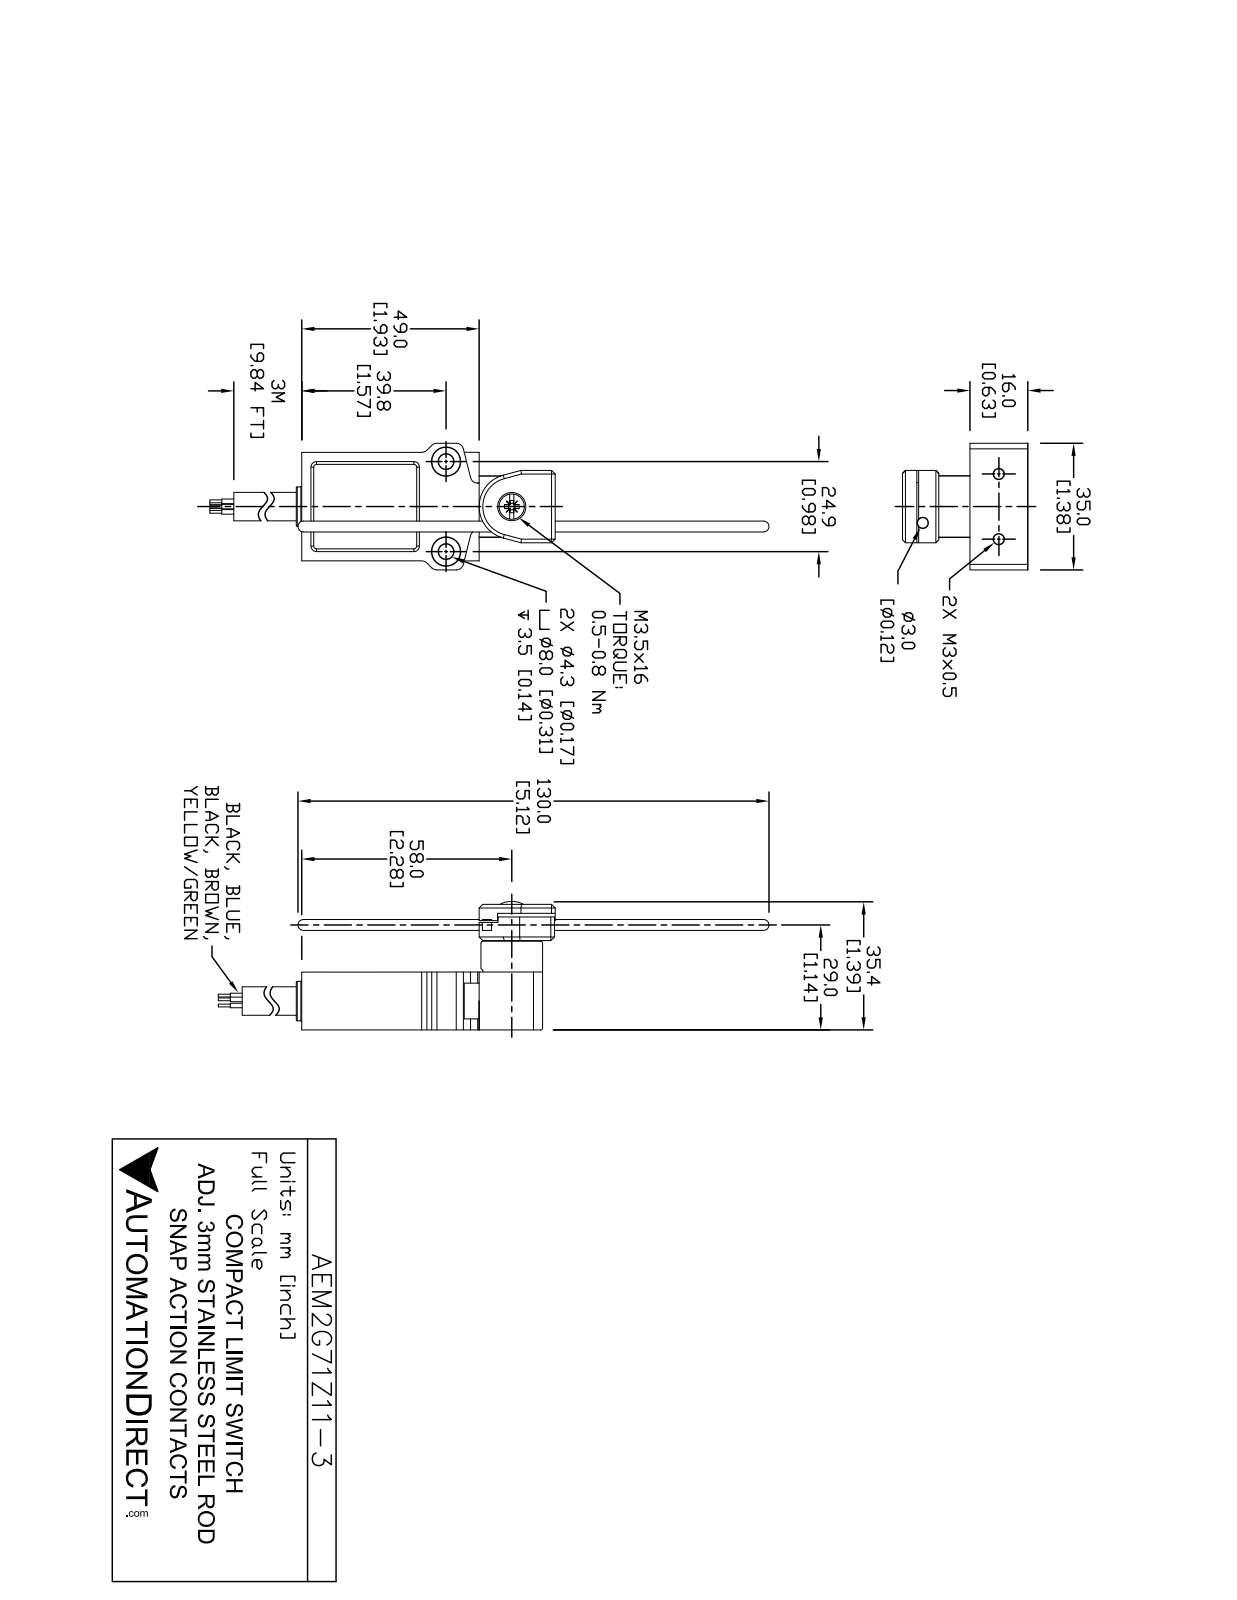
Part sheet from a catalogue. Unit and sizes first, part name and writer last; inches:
Units: inches
Overall size (bounding box): 5.634 × 1.378 × 1.374
Round holes (diameter × count): ⌀0.118 ×2, ⌀0.173 ×2, ⌀0.323 ×2, ⌀0.197 ×1, ⌀0.32 ×1
Round bosses / shafts (diameter × count): ⌀0.622 ×1, ⌀0.289 ×1, ⌀0.276 ×1, ⌀0.12 ×1
Partial cylindrical surfaces — rounded edges, fillets, slot ends (radius × count): R0.079 ×8, R0.256 ×1, R0.355 ×1
Main face-to-face distances: 0.63, 1.181, 0.354, 1.929, 0.984, 0.185, 0.18, 0.534, 1.164, 0.539
Hole centre spacings: 0.863, 0.748, 0.984
Volume: 1.979 in³ · Surface area: 18.36 in²
Bodies: 3 solids, 144 faces (91 planar, 43 cylindrical, 10 other)
Part name (STEP PRODUCT): AEM2G71Z11-3_Default
STEP written by: SolidWorks 2021 (CONFIG_CONTROL_DESIGN)
